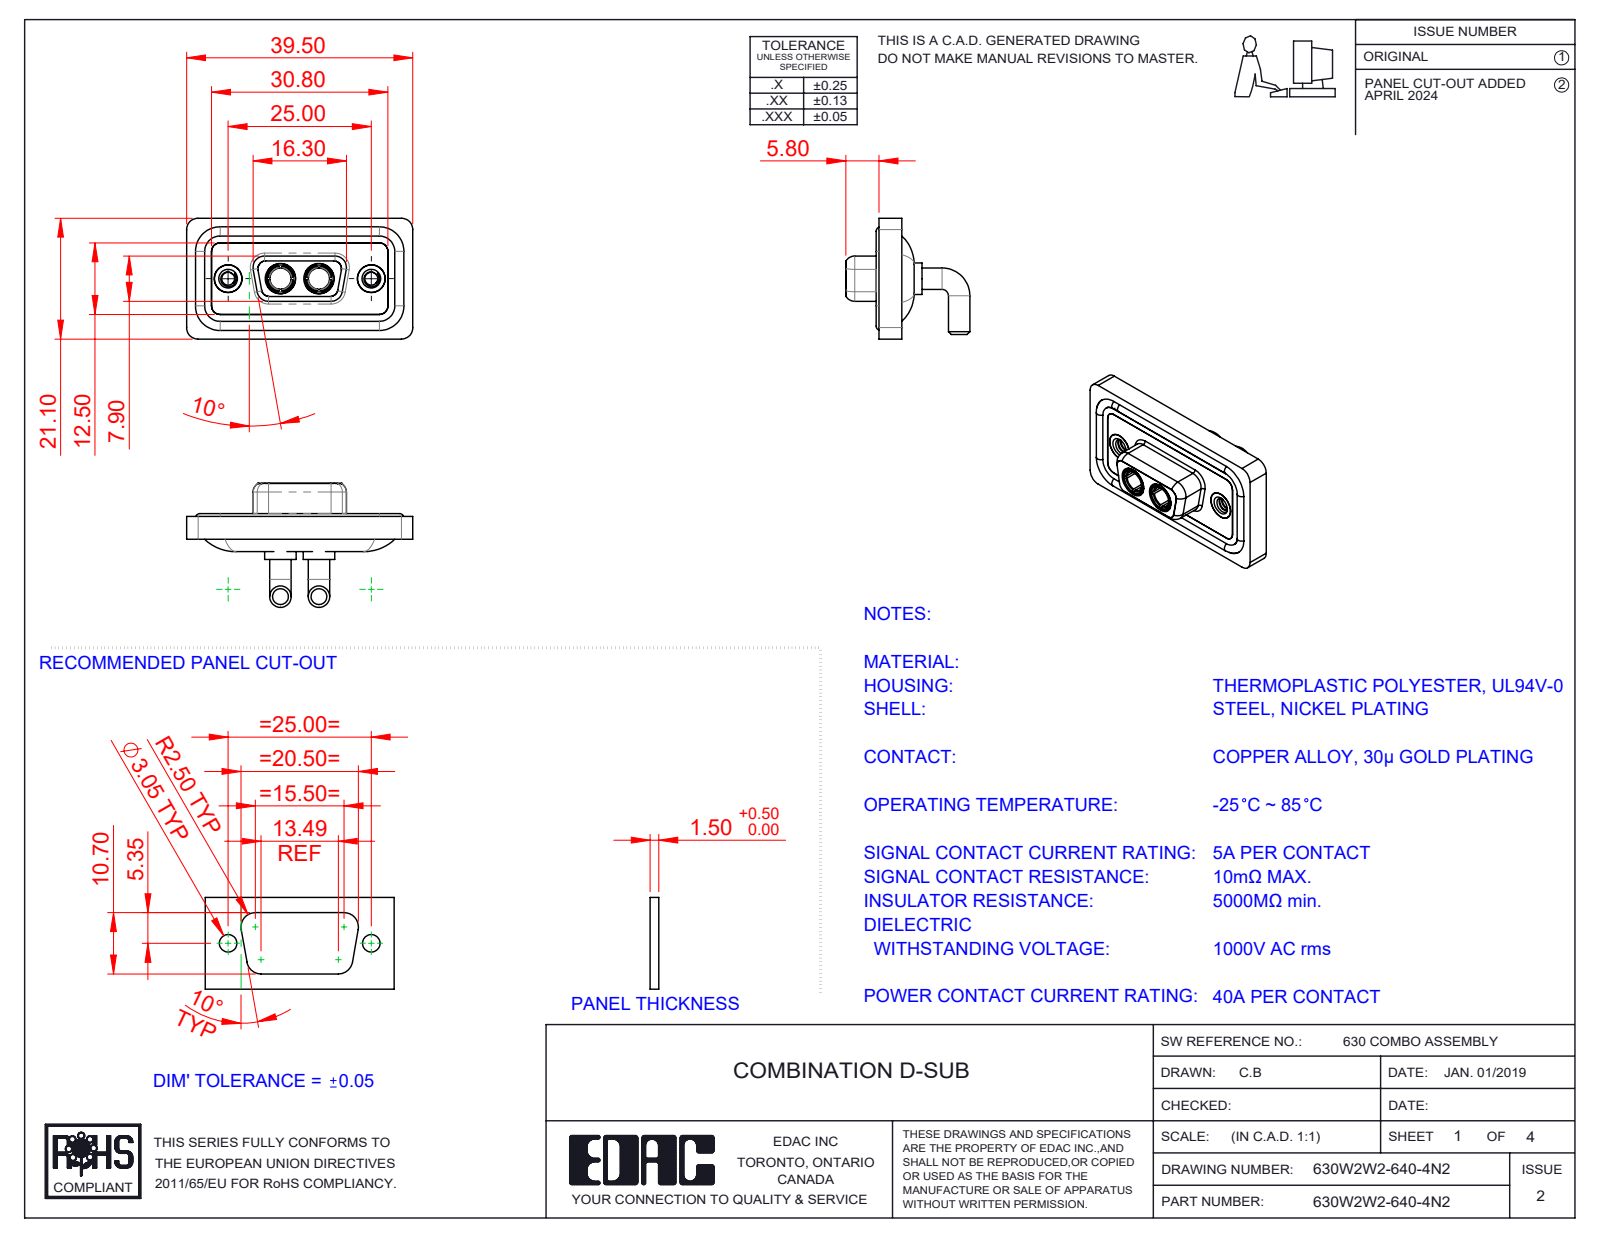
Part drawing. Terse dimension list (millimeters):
name: Power Socket_40A RA; 630Combo Shell Front_09 Contacts; 630W2W2-640-4N2; 630Combo Housing_2W2 (+3 more)
written by: SolidWorks 2023 (CONFIG_CONTROL_DESIGN)
unit: mm
bodies: 11 solids, 542 faces (163 planar, 238 cylindrical, 141 other)
size: 39.5 × 21.68 × 21.1
volume: 4 961 mm³; area: 7 873 mm²
holes: 4× ⌀4.85, 2× ⌀2.26, 2× ⌀3.7, 2× ⌀4, 2× ⌀4.05, 2× ⌀5, 2× ⌀5.3
bosses: 4× ⌀3.75, 4× ⌀1.6, 2× ⌀5.5, 2× ⌀5.2, 2× ⌀4.96, 2× ⌀4.95, 2× ⌀4.8, 2× ⌀4.75
rounds: 18× R1.5, 18× R2, 8× R1.35, 8× R1.6, 4× R0.25, 4× R0.5, 4× R0.6, 4× R0.65
face distances: 0.4, 1.8, 1.1, 2.9, 2.5, 1.6, 3.1, 2.1, 0.5, 3.7
hole spacings: 9.14, 15.86, 6.72, 25
